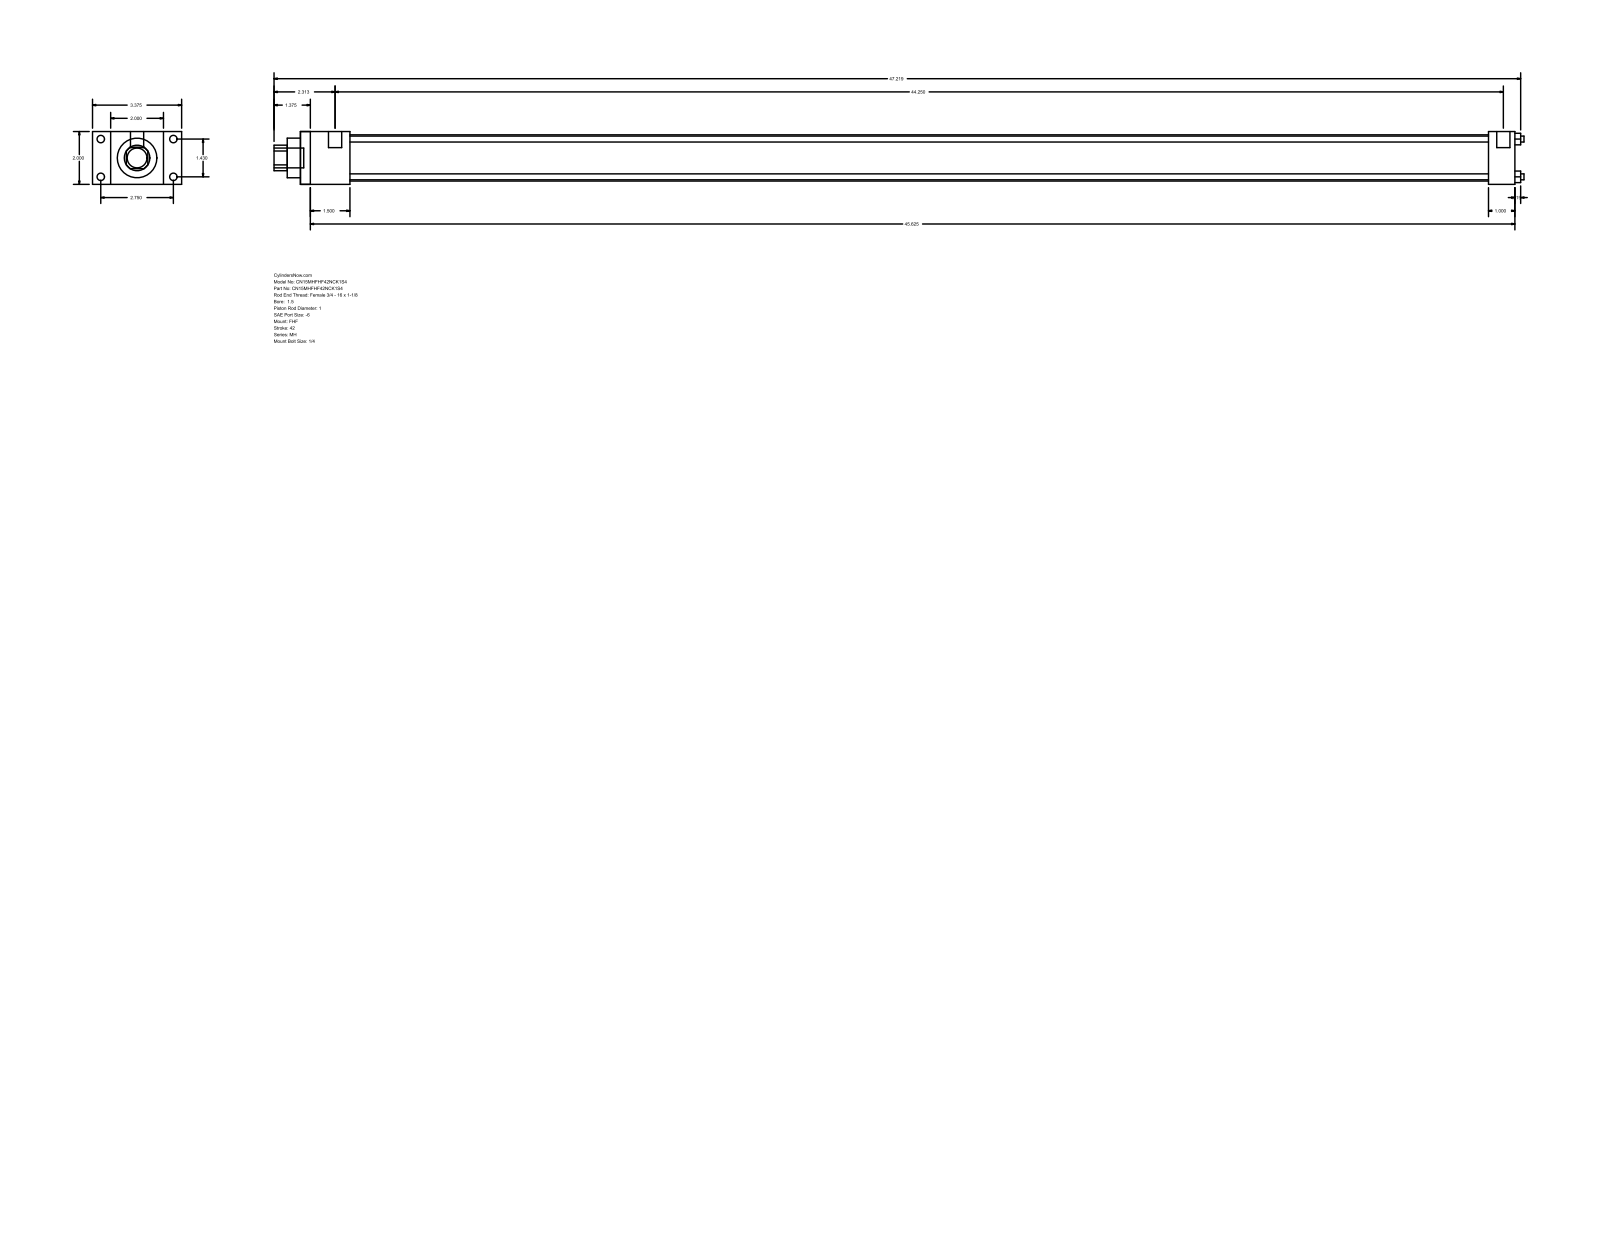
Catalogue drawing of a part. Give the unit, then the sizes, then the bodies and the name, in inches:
Units: inches
Overall size (bounding box): 47.344 × 3.375 × 2
Round holes (diameter × count): ⌀0.225 ×4, ⌀1 ×1, ⌀1.5 ×1, ⌀1.75 ×1
Round bosses / shafts (diameter × count): ⌀0.281 ×4, ⌀0.219 ×4, ⌀0.5 ×2, ⌀0.75 ×1
Partial cylindrical surfaces — rounded edges, fillets, slot ends (radius × count): R0.484 ×1
Main face-to-face distances: 2, 0.687, 2.687, 1.875, 3.375, 46, 44.125, 1, 45, 43.125
Hole centre spacings: 1.011, 1.43, 2.022
Bodies: 0 solids, 88 faces (60 planar, 28 cylindrical, 0 other)
Part name (STEP PRODUCT): MH_FHF__0150_1
STEP written by: GSSL Pune (CONFIG_CONTROL_DESIGN)
